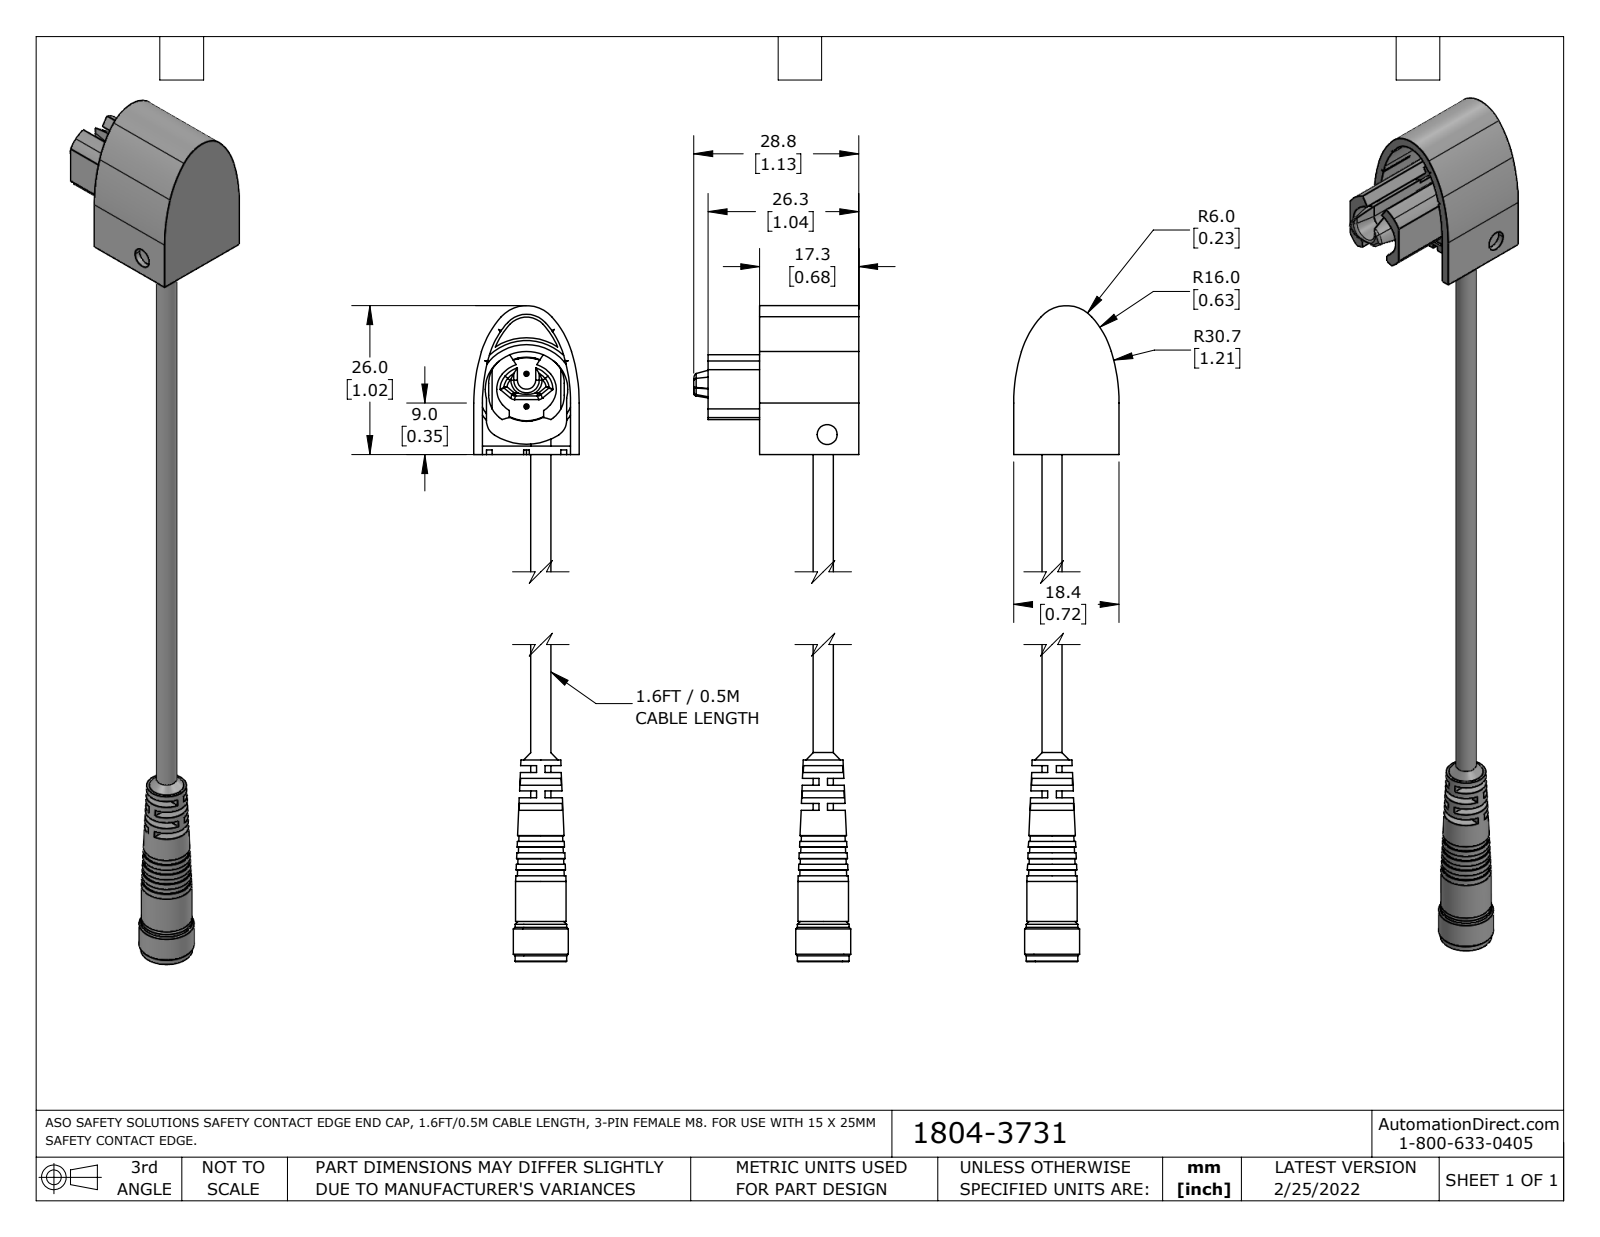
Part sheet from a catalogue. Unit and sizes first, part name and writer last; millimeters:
Units: millimetres
Overall size (bounding box): 174 × 28.8 × 18.4
Round holes (diameter × count): ⌀0.8 ×3, ⌀0.8 ×3, ⌀1.6 ×3, ⌀3.5 ×2, ⌀3.4 ×1, ⌀5.9 ×1, ⌀6.9 ×1, ⌀7.2 ×1
Round bosses / shafts (diameter × count): ⌀1.2 ×13, ⌀0.5 ×6, ⌀1 ×3, ⌀1.7 ×2, ⌀0.9 ×2, ⌀0.6 ×2, ⌀9.6 ×1, ⌀9 ×1
Partial cylindrical surfaces — rounded edges, fillets, slot ends (radius × count): R0.1 ×8, R1 ×8, R0.5 ×7, R0.3 ×6, R5 ×6, R0.4 ×2, R2.9 ×2, R3 ×2
Main face-to-face distances: 1.5, 16.9, 1, 3.2, 4.4, 8.8, 2.2, 7.6, 15.2, 1.7
Hole centre spacings: 1.8, 2.5, 3.5, 1, 1.5, 2, 2.5, 2.6
Volume: 7 830 mm³ · Surface area: 10 310 mm²
Bodies: 10 solids, 565 faces (184 planar, 237 cylindrical, 144 other)
Part name (STEP PRODUCT): 1804-3731_Default
STEP written by: SolidWorks 2021 (CONFIG_CONTROL_DESIGN)
